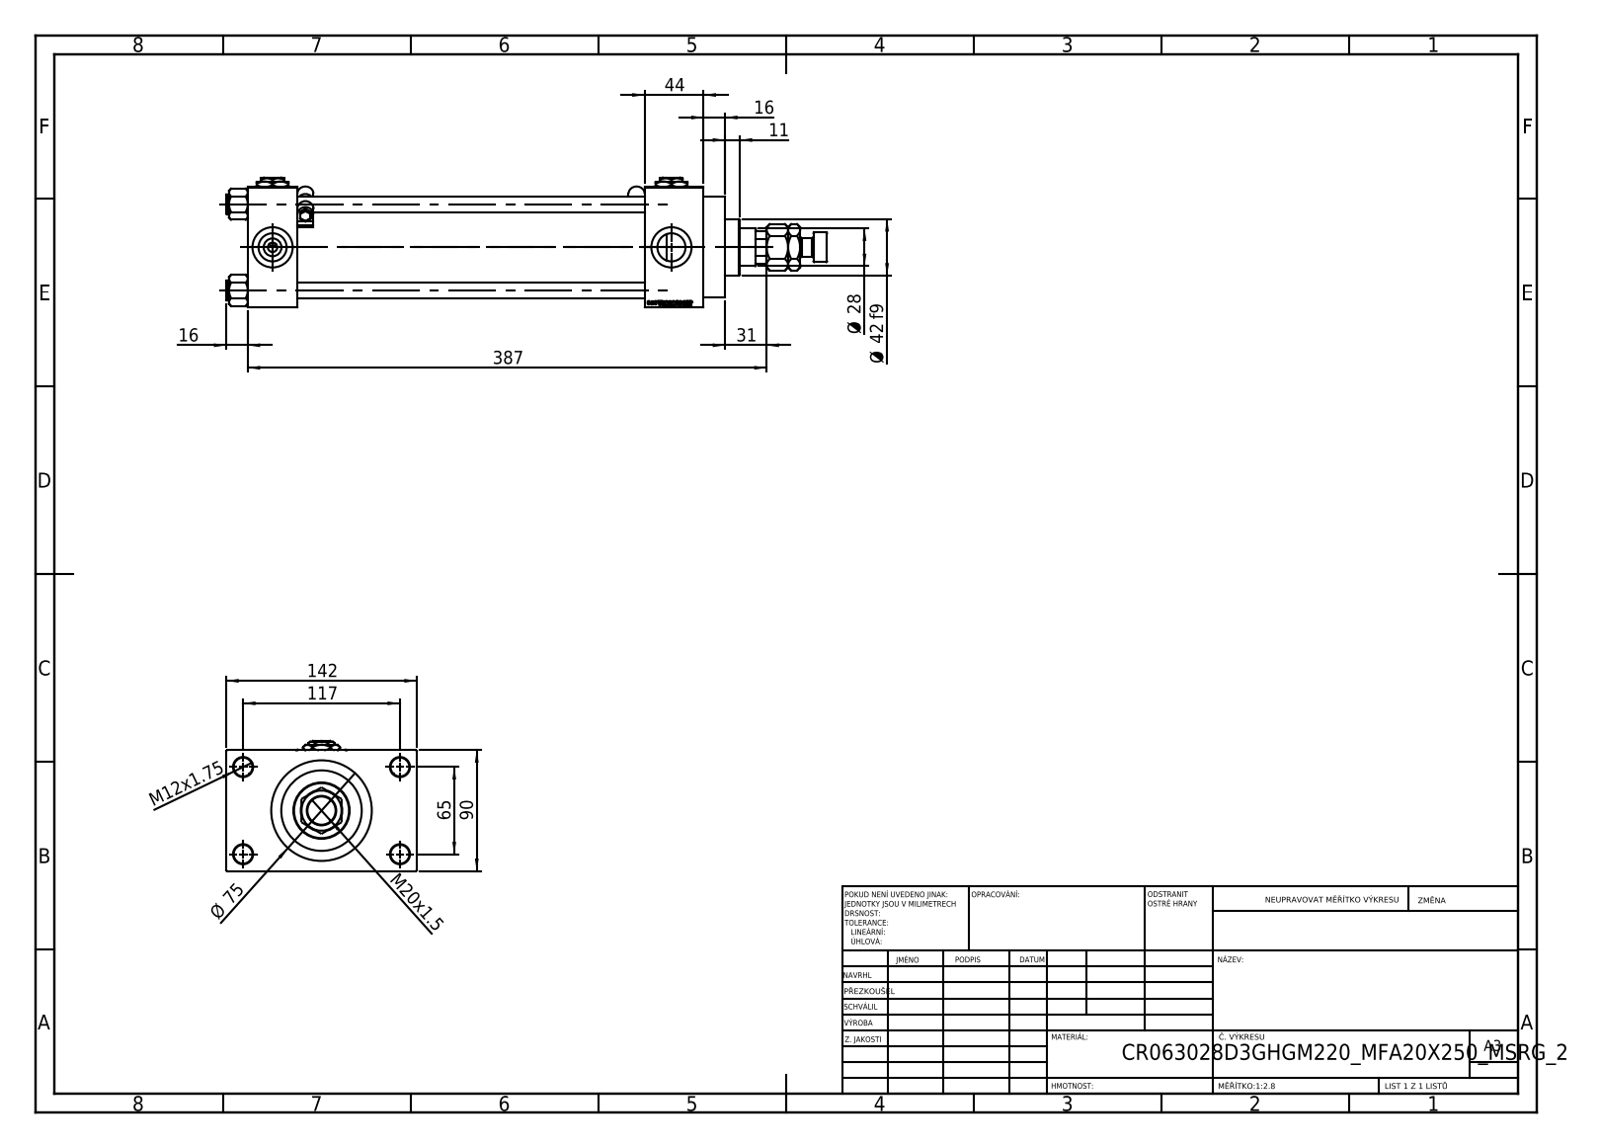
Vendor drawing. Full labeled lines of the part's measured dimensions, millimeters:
Part name (STEP PRODUCT): MFA; V215CR_VCP_D; MSRF_MSRG1; V215CR_D_TYCINKA (+4 more)
STEP written by: SolidWorks 2019 (CONFIG_CONTROL_DESIGN)
Units: millimetres
Bodies: 16 solids, 1320 faces (597 planar, 131 cylindrical, 592 other)
Overall size (bounding box): 448 × 142 × 97
Volume: 1 461 000 mm³ · Surface area: 345 716 mm²
Round holes (diameter × count): ⌀12 ×4, ⌀14 ×4, ⌀20.96 ×4, ⌀30 ×4, ⌀7 ×3, ⌀18.5 ×1, ⌀28 ×1, ⌀31 ×1, ⌀50 ×1, ⌀60 ×1, ⌀63 ×1
Round bosses / shafts (diameter × count): ⌀15 ×4, ⌀5 ×2, ⌀2.5 ×2, ⌀75 ×1, ⌀69 ×1, ⌀42 ×1, ⌀22 ×1, ⌀14 ×1
Partial cylindrical surfaces — rounded edges, fillets, slot ends (radius × count): R0.5 ×12, R6 ×4, R13.5 ×1
Main face-to-face distances: 90, 259, 37, 296, 303, 340, 44, 116, 26, 356
Hole centre spacings: 26.35, 45.47, 64.3, 66.92, 69.81, 90.65, 111.34, 65
